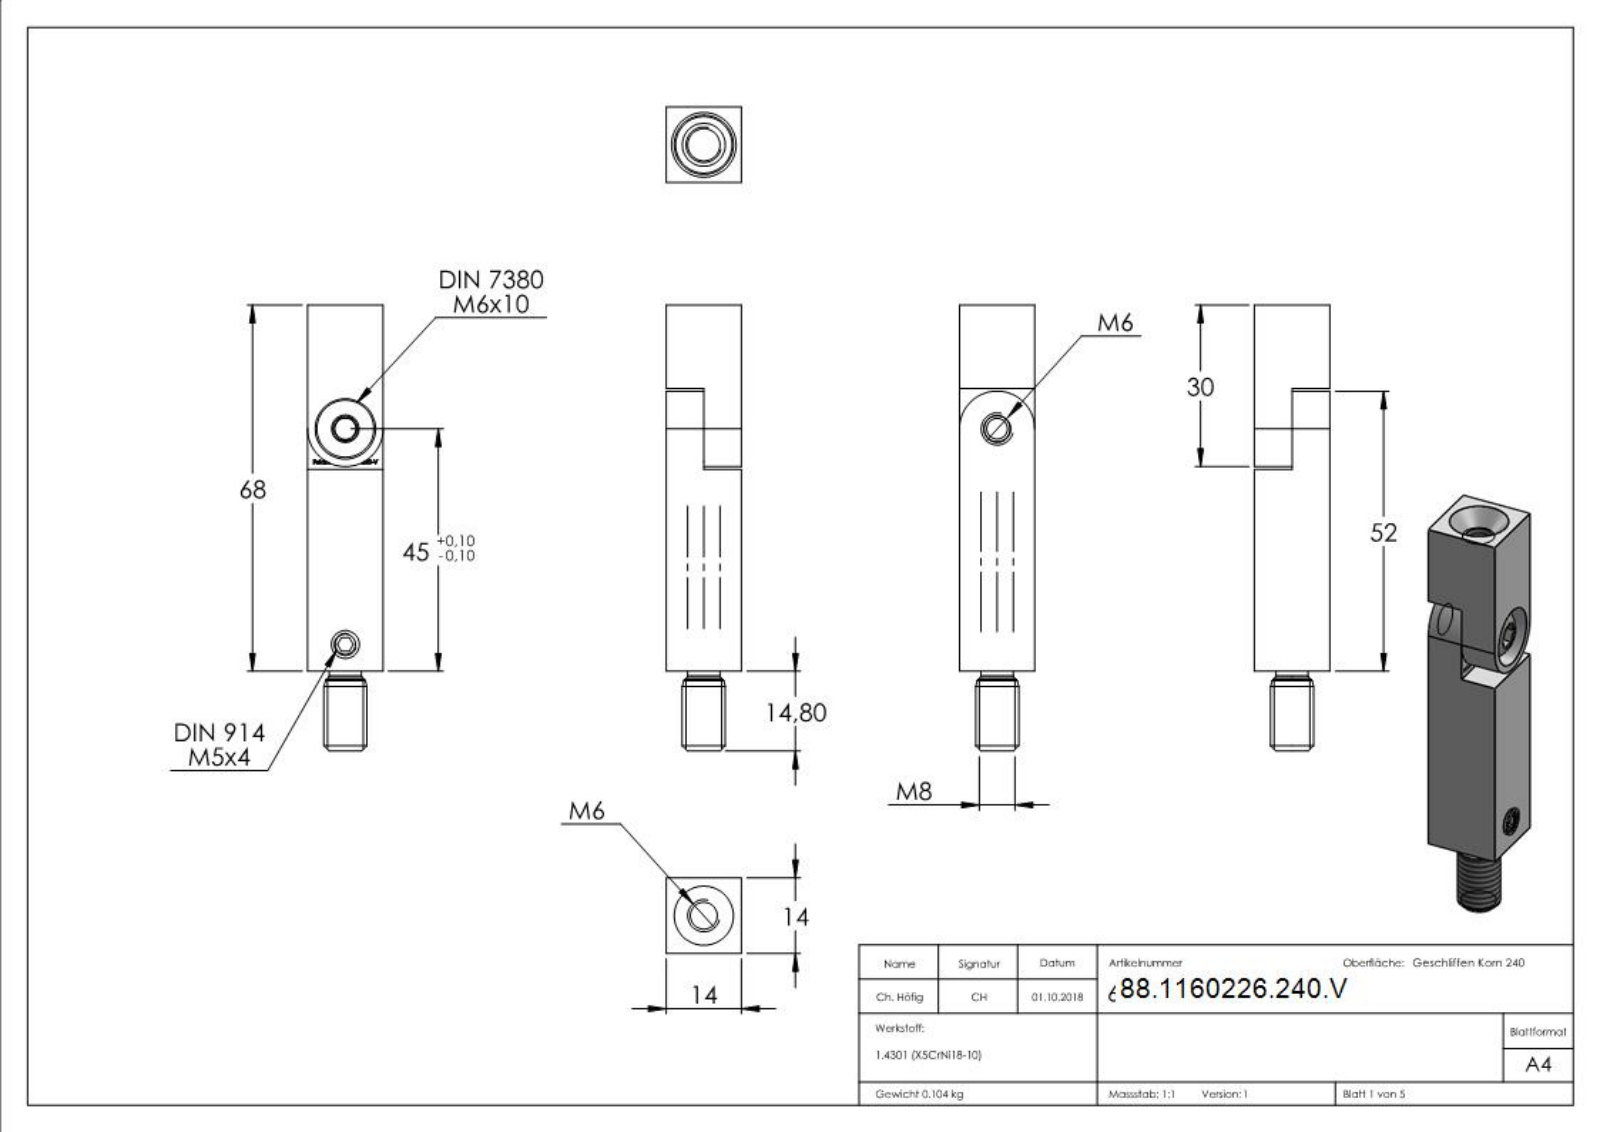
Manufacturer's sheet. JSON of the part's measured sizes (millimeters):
{"part_name": "60226-240-V; DIN914_DIN 914 M5x4; 60226-240-V Teil2_60226-240-V Teil2; ISO 7380 M6x8_ISO 7380 M6x10 (+2 more)", "step_written_by": "SolidWorks 2015 (CONFIG_CONTROL_DESIGN)", "units": "millimeters", "bodies": {"solids": 5, "faces": 374, "planar": 183, "cylindrical": 34, "other": 157}, "overall_size": [82.8, 14, 14], "volume_mm3": 13189, "surface_area_mm2": 7406, "round_holes": [[5, 2], [4.2, 1], [6.5, 1], [7.1, 1], [11, 1], [11.2, 1]], "round_bosses_or_shafts": [[14, 1], [10.6, 1], [10.5, 1], [8, 1], [7, 1], [6, 1], [5, 1], [4.77, 1]], "face_to_face_distances": [14, 7, 4, 3, 10, 15.5, 15, 30.5, 36.3, 51.3], "hole_center_spacings": [40]}
